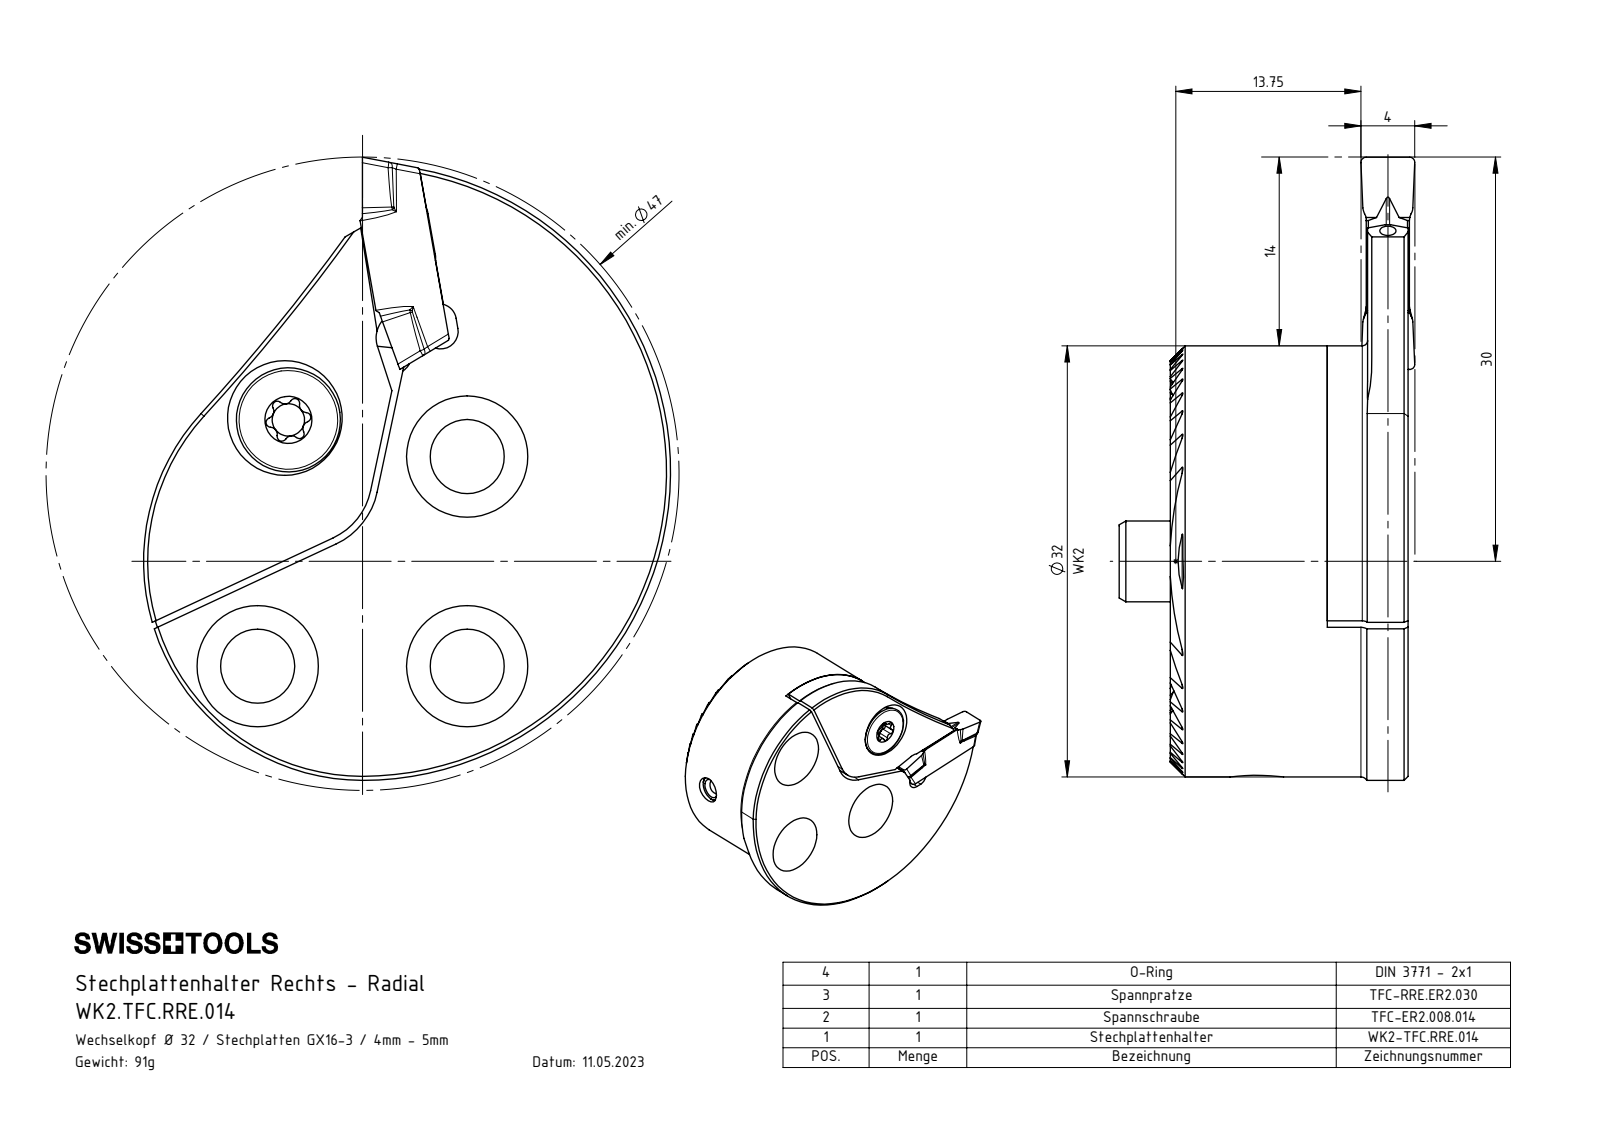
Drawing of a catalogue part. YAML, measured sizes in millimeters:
part_name: "WK2.TFC.RRE.014; TFC-ER2.008.014_A; TFC-RRE.ER2.030_A; GX16-3E4.00N0.40-M40 (+6 more)"
step_written_by: "SolidWorks 2022 (AUTOMOTIVE_DESIGN)"
units: millimeters
bodies: {solids: 9, faces: 542, planar: 203, cylindrical: 202, other: 137}
overall_size: [46.25, 39.12, 21.95]
volume: 11937
surface_area: 8609
round_holes:
  - {diameter: 5.5, count: 4}
  - {diameter: 9, count: 3}
  - {diameter: 1.2, count: 2}
  - {diameter: 4, count: 2}
  - {diameter: 4.2, count: 2}
  - {diameter: 2.4, count: 1}
  - {diameter: 2.5, count: 1}
  - {diameter: 3, count: 1}
  - {diameter: 3.3, count: 1}
  - {diameter: 6.5, count: 1}
  - {diameter: 11.98, count: 1}
round_bosses_or_shafts:
  - {diameter: 32, count: 1}
  - {diameter: 12, count: 1}
  - {diameter: 6, count: 1}
  - {diameter: 5, count: 1}
  - {diameter: 4.1, count: 1}
  - {diameter: 4, count: 1}
partial_cylinders:
  - {radius: 0.12, count: 22}
  - {radius: 0.4, count: 10}
  - {radius: 0.35, count: 6}
  - {radius: 0.54, count: 6}
  - {radius: 1, count: 4}
  - {radius: 2.3, count: 4}
  - {radius: 1.3, count: 3}
  - {radius: 2, count: 1}
face_to_face_distances: [3, 1.3, 2.6, 6, 3.9, 5.2, 6.5, 12.99, 11.69, 10.39]
hole_center_spacings: [11, 15.56, 5.5, 5.69, 8.96, 9.68, 9.76, 11.85]
